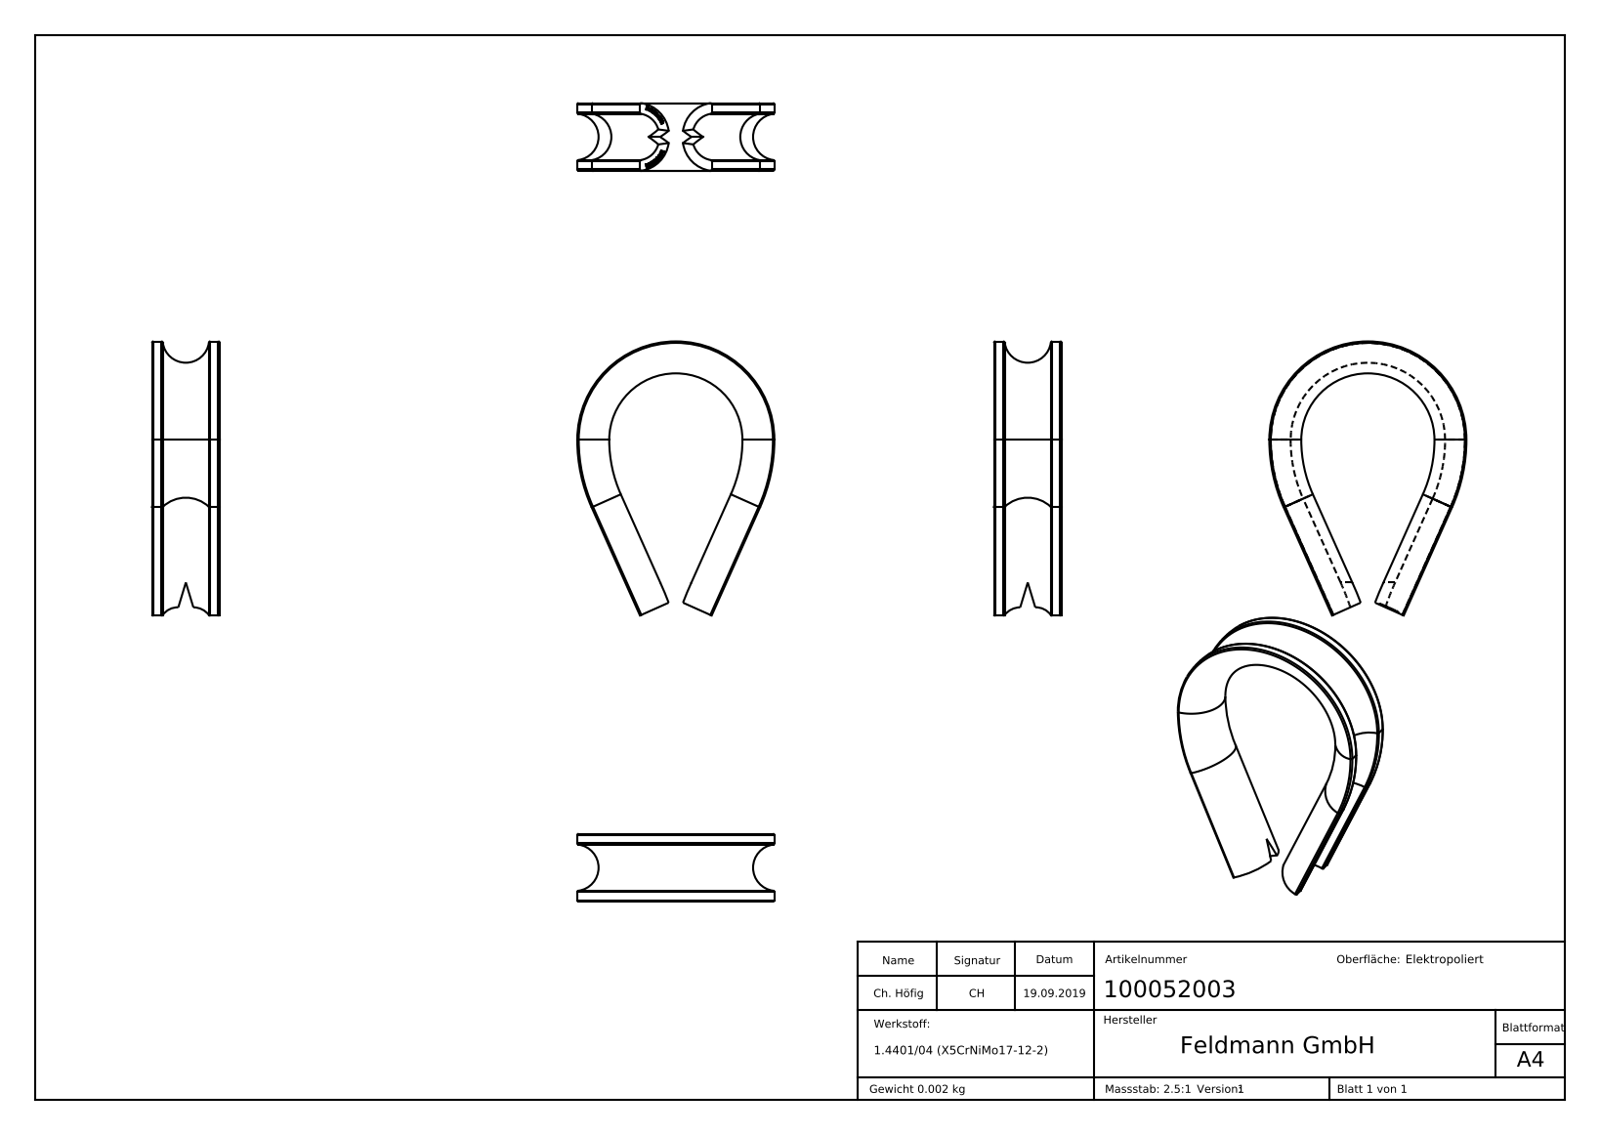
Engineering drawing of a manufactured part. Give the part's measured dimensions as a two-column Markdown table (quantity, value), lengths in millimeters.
| quantity | value |
| --- | --- |
| part name | 100052003 |
| STEP written by | SolidWorks 2015 (CONFIG_CONTROL_DESIGN) |
| units | millimeters |
| bodies | 1 solid, 277 faces (112 planar, 20 cylindrical, 145 other) |
| overall size | 20.58 × 14.8 × 5.07 |
| volume | 237 mm³ |
| surface area | 683 mm² |
| partial cylindrical surfaces (radius × count) | 0.1 × 8, 1.75 × 2, 2.55 × 2, 12.4 × 2, 7.4 × 1 |
